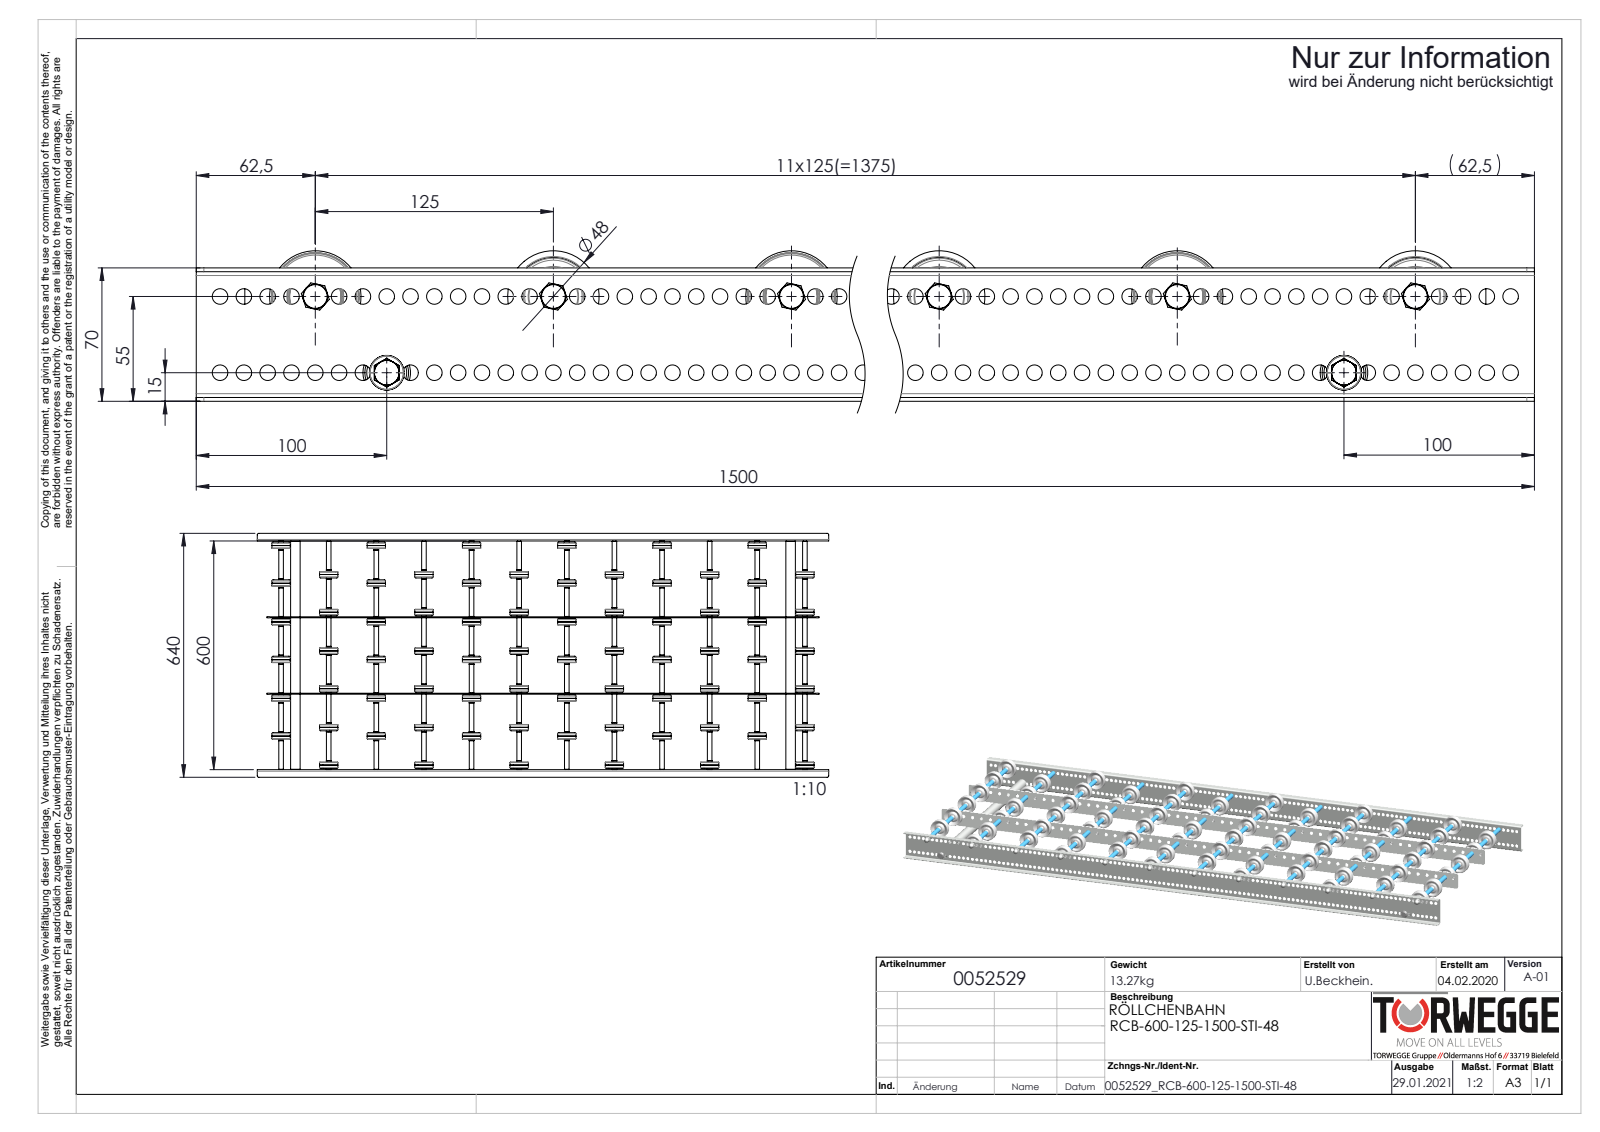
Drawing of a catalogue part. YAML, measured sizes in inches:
part_name: "Hutmutter_DIN_1587_M8; Profil_LRB-20x70x20x2_KFG_S100201_U-PROFIL-20-70-20-2-LRB-L=1500; Röllchenachse-für-Konfiguration_EL600 Stahl; Traversen_KFG_L600 (+6 more)"
step_written_by: "SolidWorks 2020 (AUTOMOTIVE_DESIGN)"
units: inches
bodies: {solids: 266, faces: 8444, planar: 1644, cylindrical: 3528, other: 3272}
overall_size: [59.055, 25.197, 3.11]
volume: 194.2
surface_area: 3892
round_holes:
  - {diameter: 0.323, count: 238}
  - {diameter: 0.335, count: 58}
  - {diameter: 0.262, count: 12}
  - {diameter: 0.315, count: 12}
  - {diameter: 0.38, count: 12}
  - {diameter: 0.591, count: 12}
  - {diameter: 1.614, count: 12}
  - {diameter: 0.268, count: 2}
  - {diameter: 0.827, count: 2}
round_bosses_or_shafts:
  - {diameter: 1.89, count: 12}
  - {diameter: 0.512, count: 12}
  - {diameter: 0.492, count: 12}
  - {diameter: 0.488, count: 12}
  - {diameter: 0.472, count: 12}
  - {diameter: 0.453, count: 12}
  - {diameter: 0.984, count: 2}
  - {diameter: 0.315, count: 2}
partial_cylinders:
  - {radius: 0.157, count: 8}
  - {radius: 0.079, count: 4}
  - {radius: 0.197, count: 4}
face_to_face_distances: [7.894, 0.079, 23.701, 15.787, 2.992, 3.898, 0.098, 7.795, 2.677, 0.472]
hole_center_spacings: [0.492, 0.984, 1.476, 1.969, 2.461, 2.953, 3.445, 3.937]
